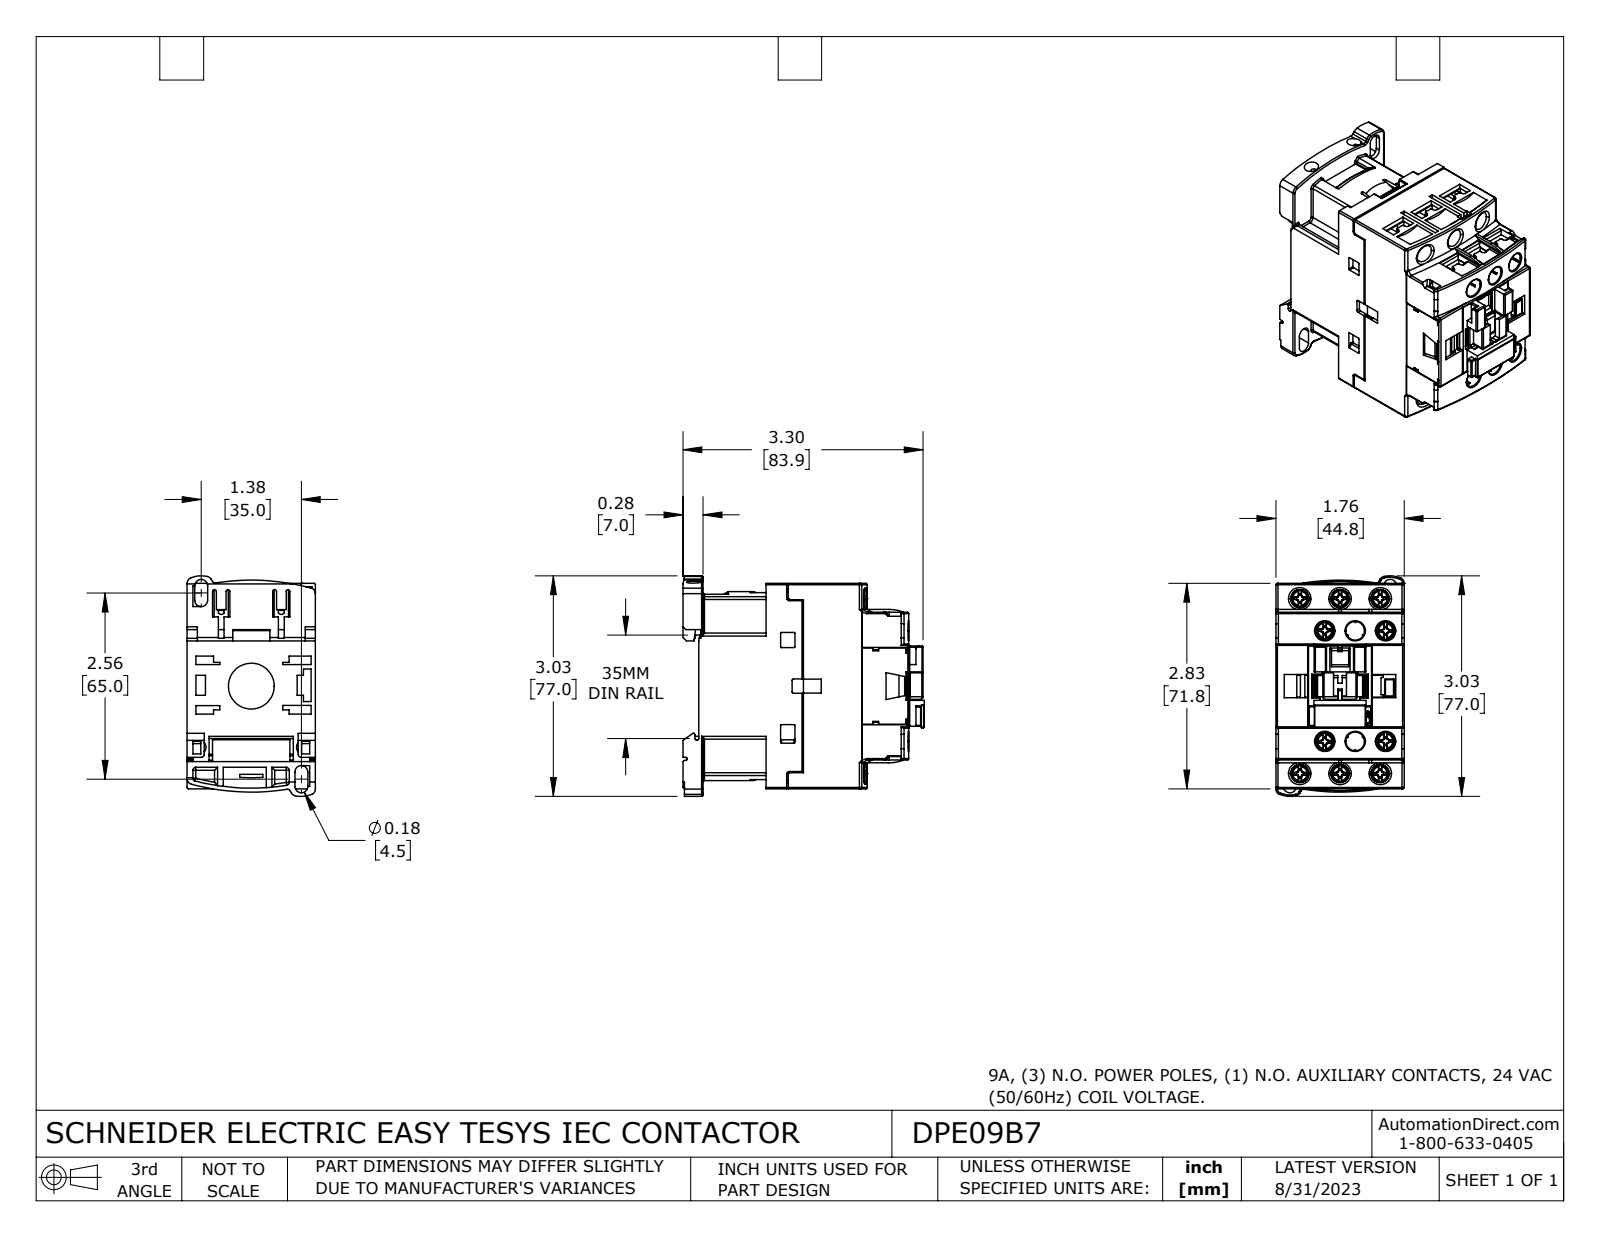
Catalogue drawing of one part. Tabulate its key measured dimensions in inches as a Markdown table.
| quantity | value |
| --- | --- |
| part name | DPE09B7 |
| STEP written by | SolidWorks 2021 (CONFIG_CONTROL_DESIGN) |
| units | inches |
| bodies | 20 solids, 3363 faces (2297 planar, 694 cylindrical, 372 other) |
| overall size | 3.317 × 3.031 × 1.783 |
| volume | 8.907 in³ |
| surface area | 103.4 in² |
| round holes (diameter × count) | 0.252 × 6, 0.256 × 6, 0.197 × 2, 0.167 × 1, 0.63 × 1 |
| round bosses / shafts (diameter × count) | 0.138 × 10, 0.108 × 10, 0.315 × 6 |
| partial cylindrical surfaces (radius × count) | 0.02 × 78, 0.012 × 64, 0.039 × 61, 0.006 × 42, 0.016 × 24, 0.63 × 9, 0.024 × 8, 0.079 × 7 |
| main face-to-face distances | 0.047, 1.764, 1.717, 0.321, 1.128, 0.807, 0.35, 2.78, 1.366, 1.118 |
| hole center spacings | 0.417, 0.488, 0.551, 0.558, 0.788, 0.878, 1.321, 1.576 |
